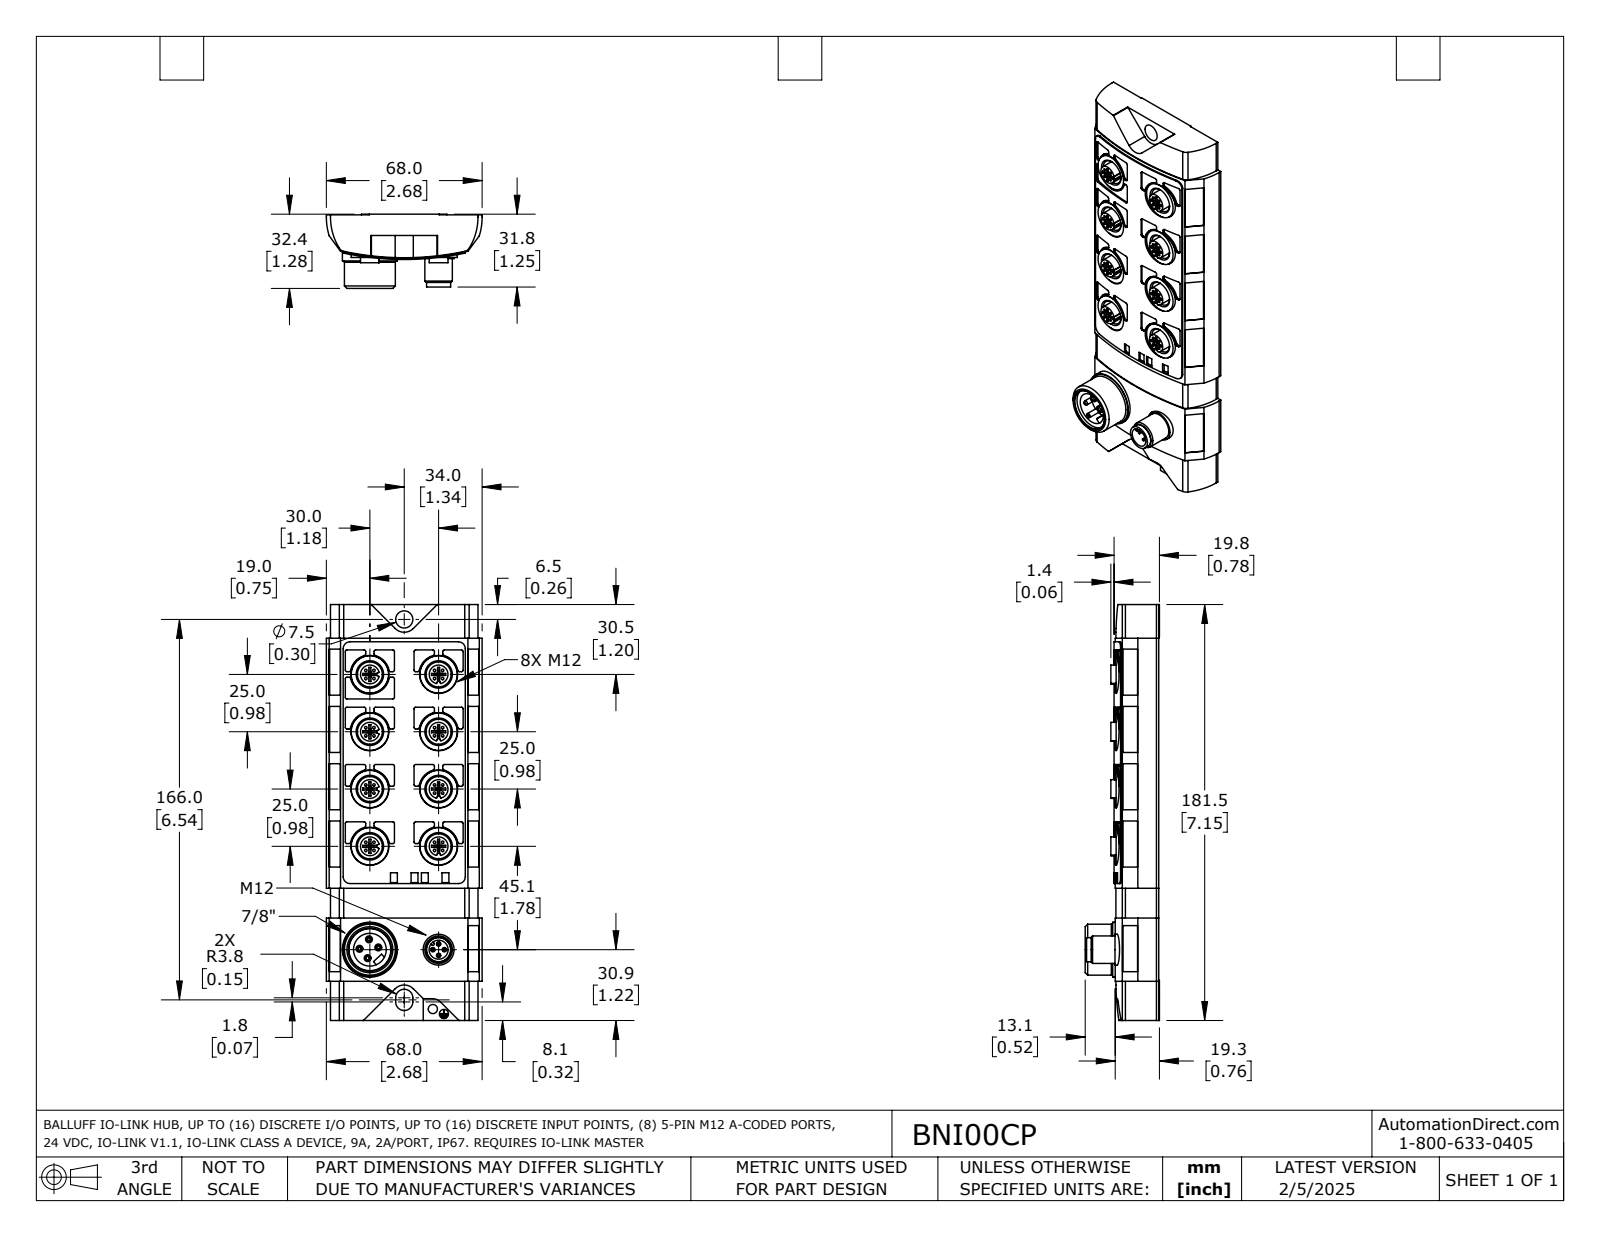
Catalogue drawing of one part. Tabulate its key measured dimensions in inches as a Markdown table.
| quantity | value |
| --- | --- |
| part name | BNI00CP |
| STEP written by | SolidWorks 2021 (AUTOMOTIVE_DESIGN) |
| units | inches |
| bodies | 1 solid, 875 faces (406 planar, 429 cylindrical, 40 other) |
| overall size | 7.146 × 2.677 × 1.276 |
| volume | 12.42 in³ |
| surface area | 67.62 in² |
| round holes (diameter × count) | 0.043 × 40, 0.43 × 8, 0.654 × 8, 0.075 × 4, 0.157 × 2, 0.295 × 1, 0.327 × 1, 0.563 × 1, 0.72 × 1 |
| round bosses / shafts (diameter × count) | 0.642 × 8, 0.323 × 8, 0.118 × 4, 0.039 × 4, 0.078 × 3, 0.945 × 1, 0.875 × 1, 0.531 × 1 |
| partial cylindrical surfaces (radius × count) | 0.028 × 86, 0.031 × 40, 0.008 × 16, 0.339 × 8, 0.012 × 5, 0.117 × 3, 0.118 × 3, 0.148 × 2 |
| main face-to-face distances | 0.732, 7.146, 0.744, 0.488, 0.378, 0.354, 0.476, 0.256, 0.366, 0.122 |
| hole center spacings | 0.098, 0.139, 0.984, 0.917, 1.056, 2.296, 0.197, 0.994 |
